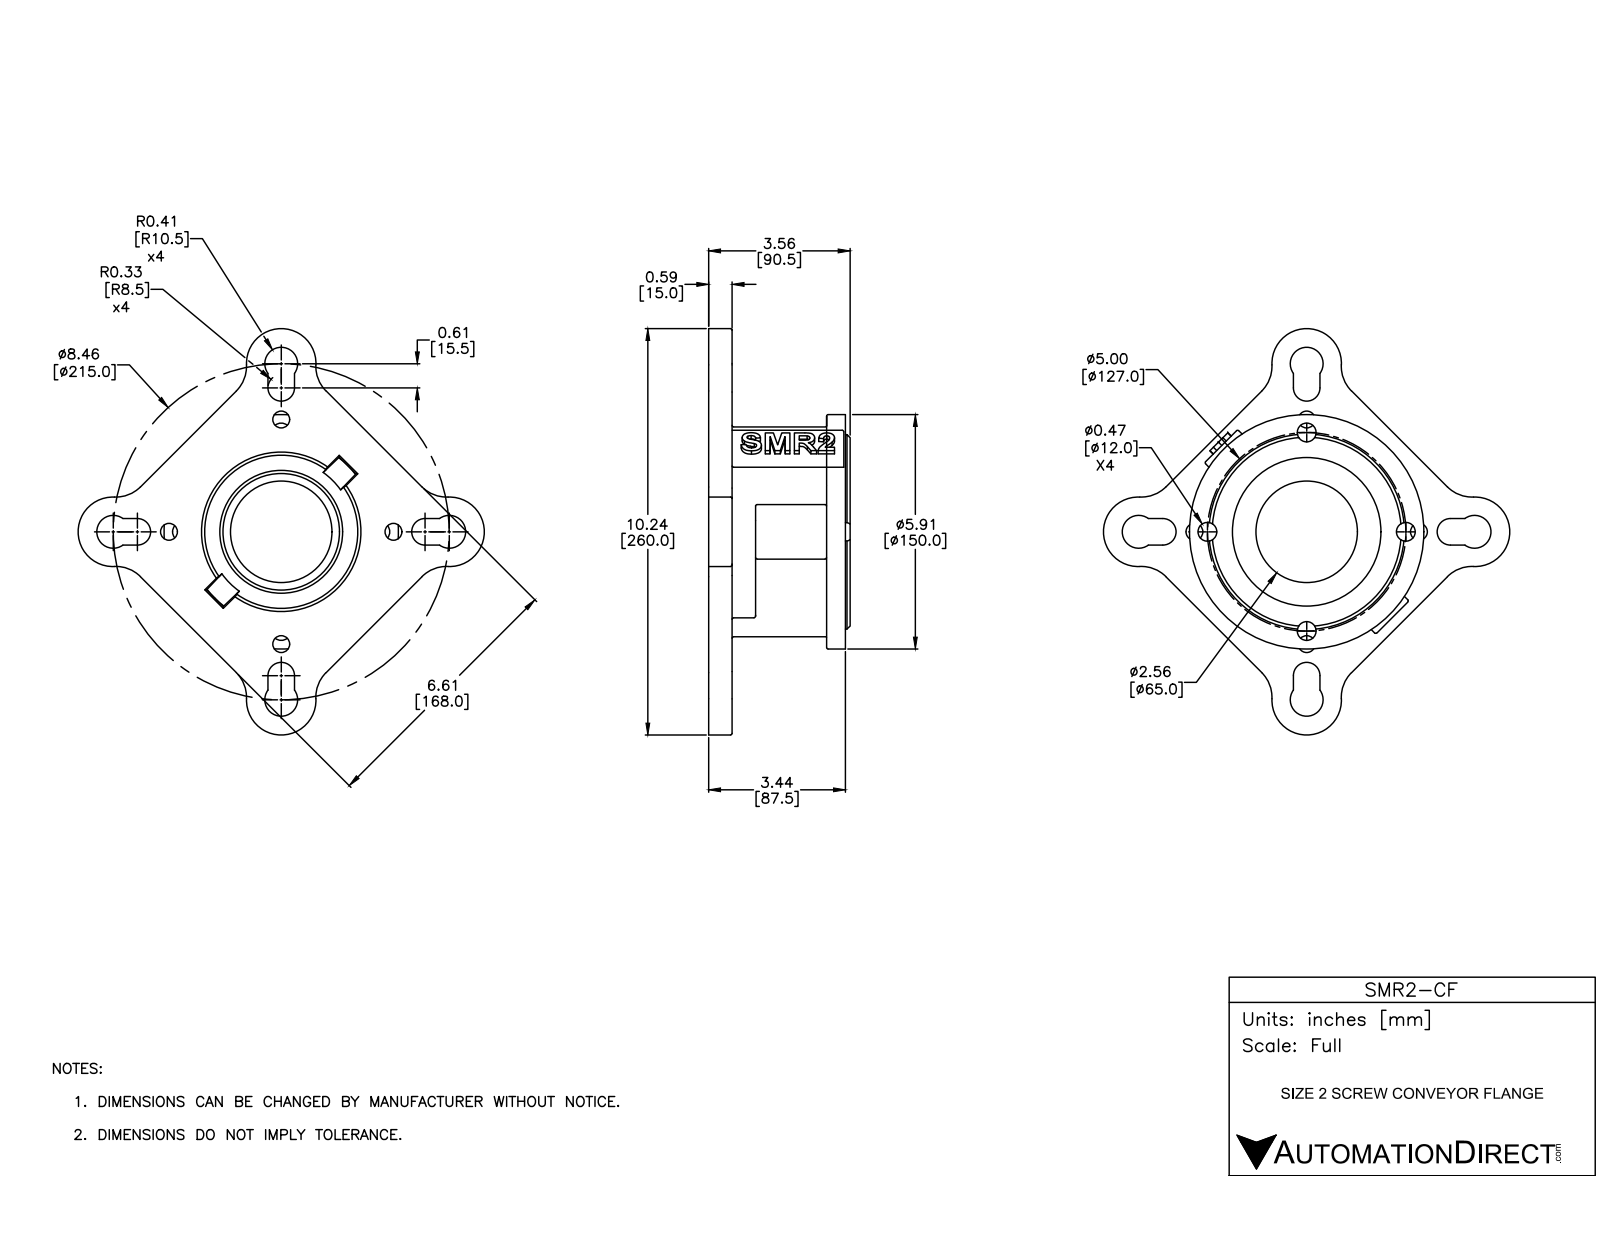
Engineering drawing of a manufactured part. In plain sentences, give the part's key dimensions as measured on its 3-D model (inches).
The part is named "SMR2-CF". Its 3-D file was written by "SolidWorks 2016 (AUTOMOTIVE_DESIGN)". It is 1 solid with 311 faces: 80 planar, 110 cylindrical and 121 other. Overall it measures 10.235 by 10.235 by 3.563 inches. Its volume is 44.97 cubic inches and its surface area 194.8 square inches. Round holes: 4 of diameter 0.422, 4 of diameter 0.472, 1 of diameter 2.559, 1 of diameter 2.937, 1 of diameter 3.74, 1 of diameter 3.858. Round bosses or shafts: 1 of diameter 5.906, 1 of diameter 4.921. Partial cylindrical surfaces (rounded edges, fillets, slot ends): 22 of radius 0.039, 12 of radius 0.875, 8 of radius 0.315, 4 of radius 0.335, 4 of radius 0.413, 4 of radius 0.591, 1 of radius 2.165. The main face-to-face distances are 0.591, 2.382, 2.972, 1.181, 1.791, 0.472, 2.264, 2.854, 3.445, 0.118. The hole center spacings are 3.775, 0.328, 2.5, 2.828, 3.535, 4, 5.328, 5.
